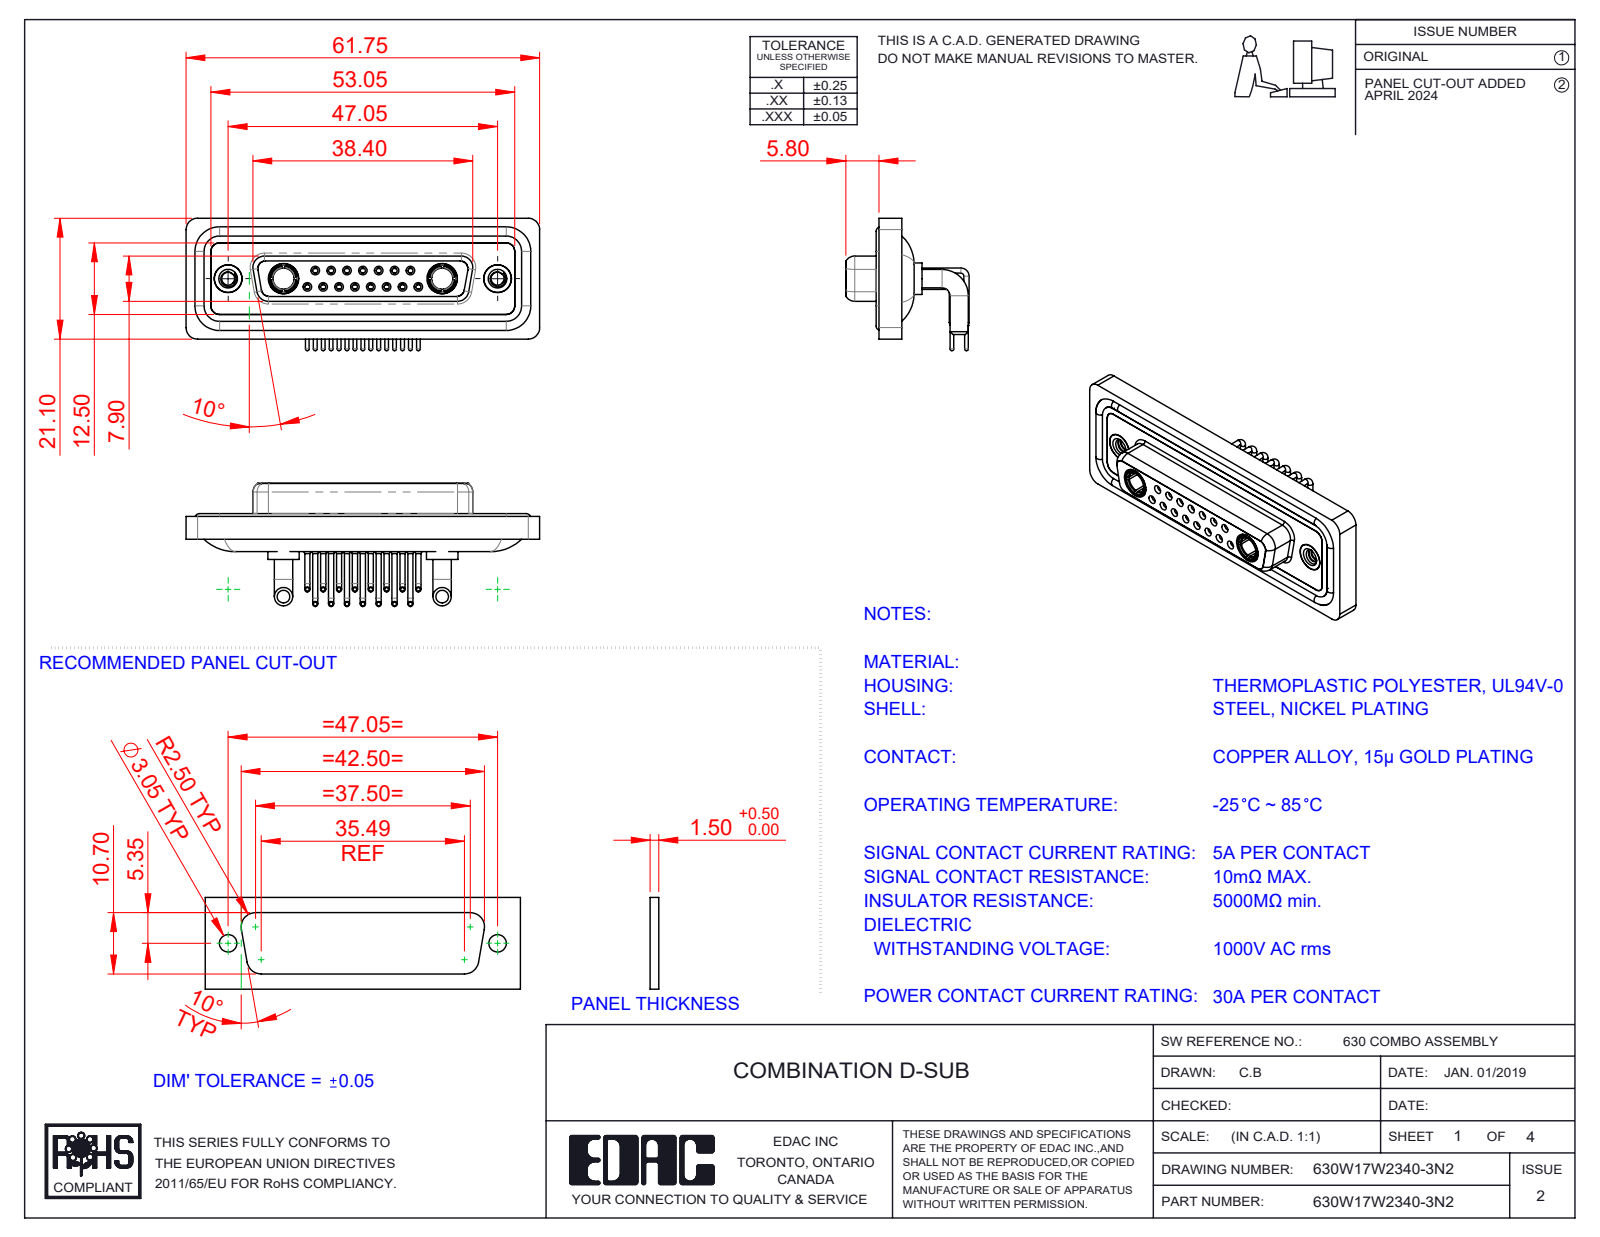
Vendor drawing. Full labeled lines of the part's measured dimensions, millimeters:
Part name (STEP PRODUCT): Power Socket_30A RA; 630Combo Contact Row 1_50 Contacts; 630Combo Threaded Rivet_2; 630Combo Contact Row 2_50 Contacts (+5 more)
STEP written by: SolidWorks 2023 (CONFIG_CONTROL_DESIGN)
Units: millimetres
Bodies: 26 solids, 1337 faces (388 planar, 583 cylindrical, 366 other)
Overall size (bounding box): 61.75 × 23.12 × 21.53
Volume: 8 543 mm³ · Surface area: 14 567 mm²
Round holes (diameter × count): ⌀0.9 ×15, ⌀1.1 ×15, ⌀1.5 ×15, ⌀2 ×15, ⌀1.6 ×8, ⌀1.7 ×7, ⌀4.85 ×4, ⌀2.26 ×2, ⌀3.7 ×2, ⌀4 ×2, ⌀4.05 ×2, ⌀5 ×2
Round bosses / shafts (diameter × count): ⌀0.9 ×15, ⌀0.65 ×15, ⌀1.6 ×11, ⌀3.2 ×4, ⌀5.5 ×2, ⌀5.2 ×2, ⌀4.96 ×2, ⌀4.95 ×2
Partial cylindrical surfaces — rounded edges, fillets, slot ends (radius × count): R1.5 ×18, R2 ×18, R1.35 ×8, R1.6 ×8, R0.25 ×4, R0.5 ×4, R0.6 ×4, R0.65 ×4
Main face-to-face distances: 0.4, 1.8, 4.1, 1.1, 1.6, 3.1, 2.5, 1.5, 3.7, 1.4
Hole centre spacings: 3.16, 2.77, 5.54, 8.31, 5.04, 7.49, 11.08, 5.03
